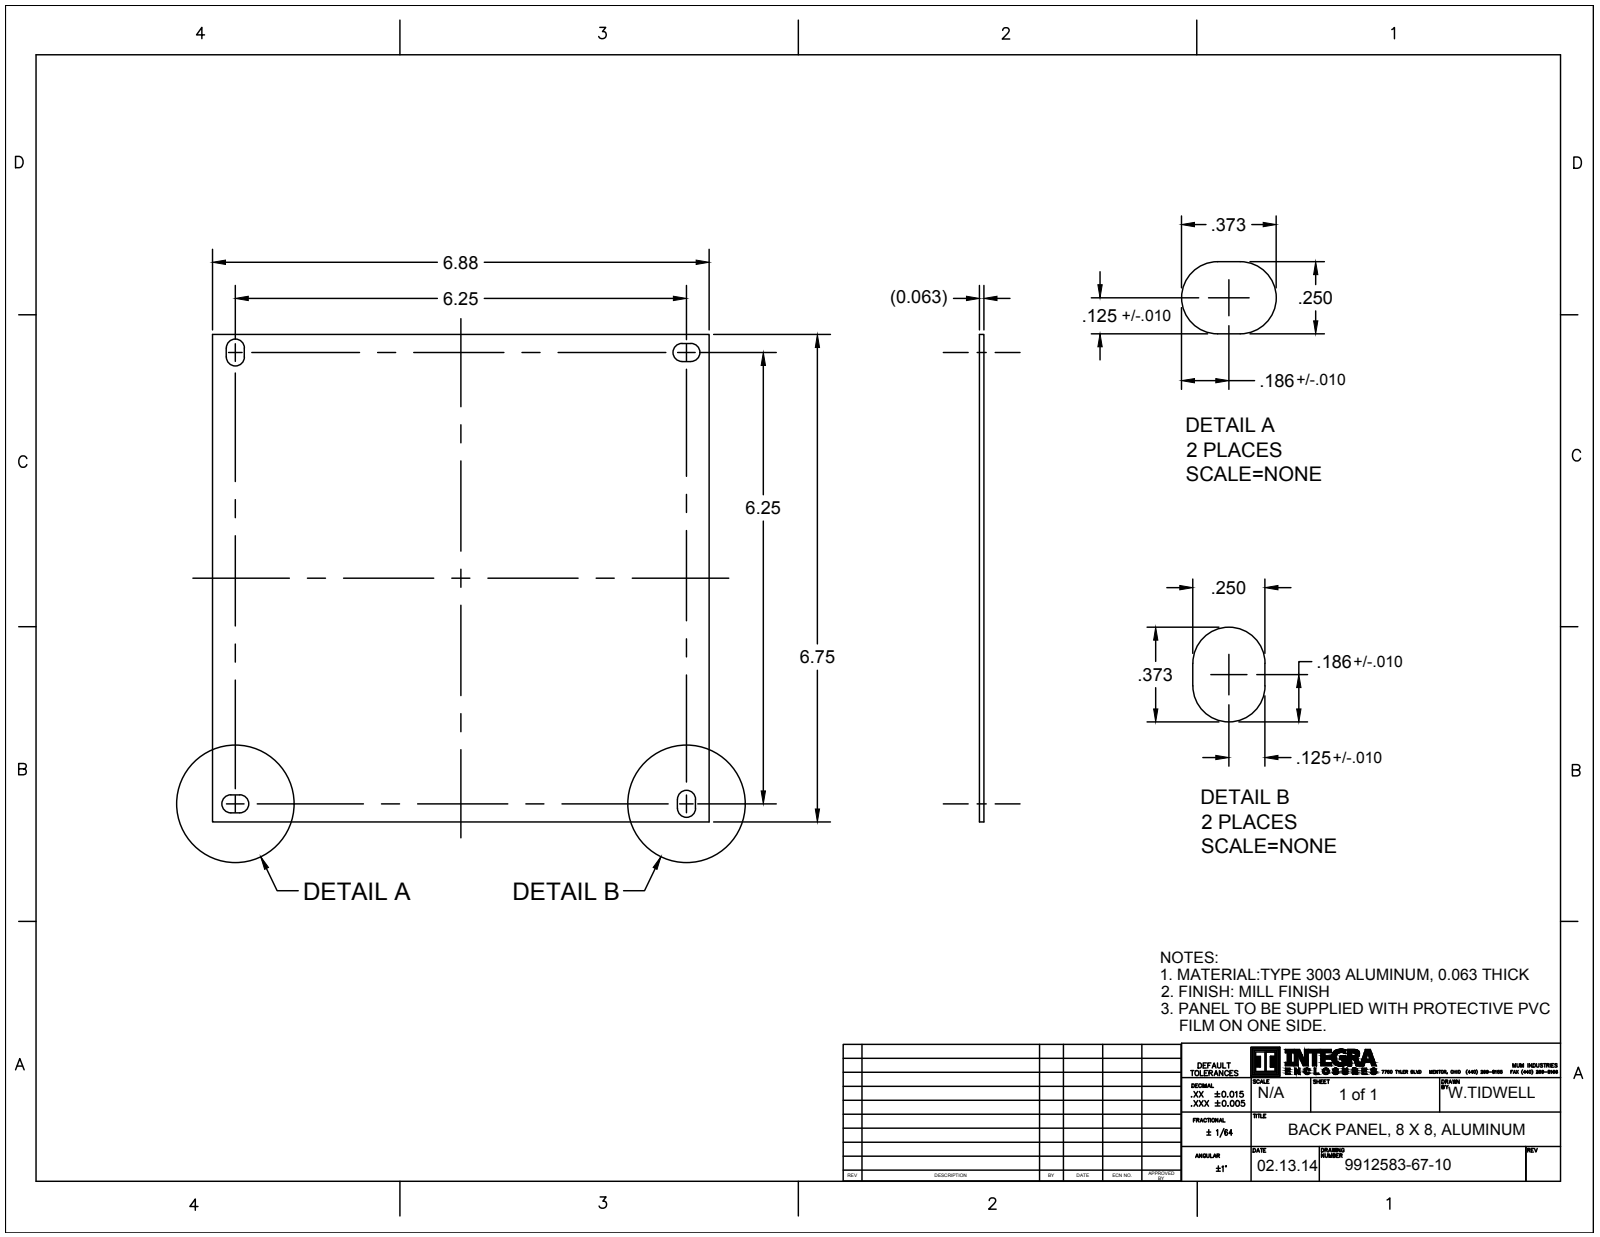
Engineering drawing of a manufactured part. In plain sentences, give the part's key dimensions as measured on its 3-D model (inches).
The part is named "9912583-67-10; 9912518-82-10; ABP88_ASM". Its 3-D file was written by "CREO PARAMETRIC BY PTC INC, 2016050 (CONFIG_CONTROL_DESIGN)". It is 5 solids with 430 faces: 90 planar, 268 cylindrical and 72 other. Overall it measures 6.88 by 6.75 by 0.443 inches. Its volume is 2.973 cubic inches and its surface area 96.74 square inches. Round bosses or shafts: 4 of diameter 0.373, 4 of diameter 0.19, 4 of diameter 0.149. Partial cylindrical surfaces (rounded edges, fillets, slot ends): 48 of radius 0.004, 8 of radius 0.125. The main face-to-face distances are 0.063, 6.75, 6.88, 0.25, 0.313, 6.225, 2.381, 5.75, 0.25, 6.25.
